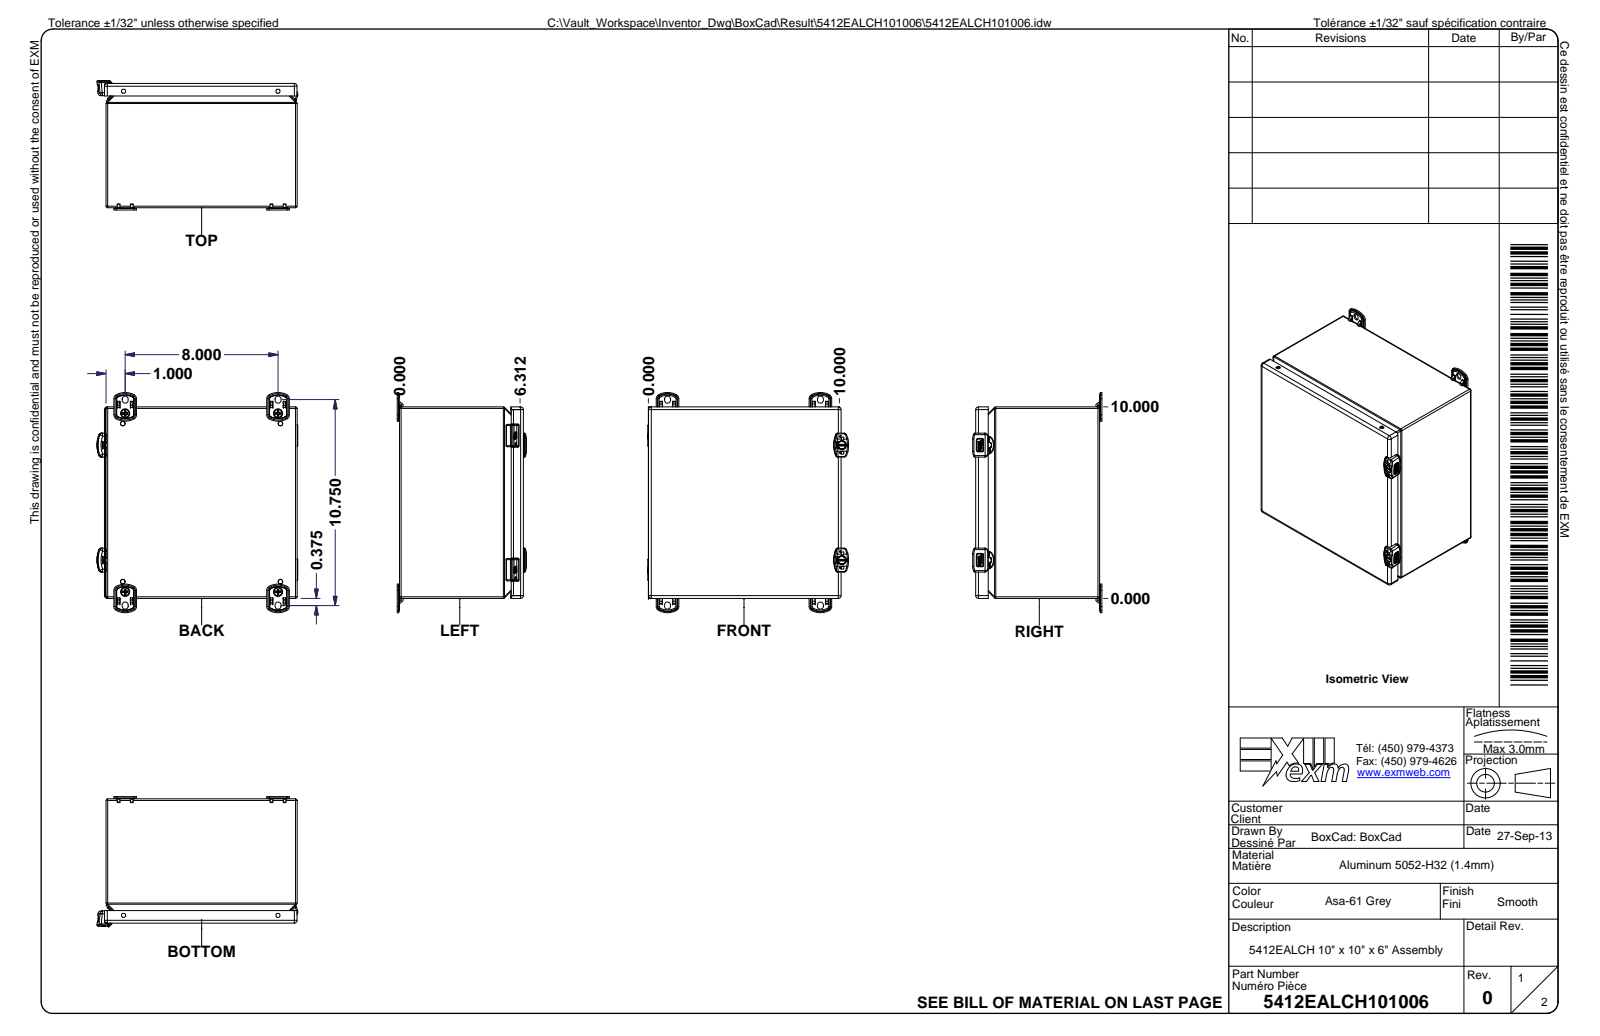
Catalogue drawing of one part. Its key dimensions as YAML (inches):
part_name: "5412EALCH101006; 5412EALCH101006B; 5412EALCH101006B-P; RIVET_NUT_SS_M6_FH_CE (+8 more)"
step_written_by: "Autodesk Inventor 2024 (AUTOMOTIVE_DESIGN)"
units: inches
bodies: {solids: 53, faces: 7459, planar: 3251, cylindrical: 1778, other: 2430}
overall_size: [11.496, 10.441, 6.756]
volume: 34.84
surface_area: 1244
round_holes:
  - {diameter: 0.197, count: 4}
  - {diameter: 0.197, count: 4}
  - {diameter: 0.236, count: 4}
  - {diameter: 0.32, count: 4}
  - {diameter: 0.03, count: 2}
  - {diameter: 0.165, count: 2}
  - {diameter: 0.173, count: 2}
  - {diameter: 0.175, count: 2}
  - {diameter: 0.201, count: 2}
  - {diameter: 0.218, count: 2}
  - {diameter: 0.23, count: 2}
  - {diameter: 0.236, count: 2}
round_bosses_or_shafts:
  - {diameter: 0.232, count: 8}
  - {diameter: 0.5, count: 4}
  - {diameter: 0.236, count: 4}
  - {diameter: 0.197, count: 3}
  - {diameter: 0.412, count: 2}
  - {diameter: 0.394, count: 2}
  - {diameter: 0.33, count: 2}
  - {diameter: 0.3, count: 2}
partial_cylinders:
  - {radius: 0.008, count: 224}
  - {radius: 0.02, count: 187}
  - {radius: 0.01, count: 100}
  - {radius: 0.004, count: 97}
  - {radius: 0.039, count: 89}
  - {radius: 0.059, count: 59}
  - {radius: 0.031, count: 33}
  - {radius: 0.012, count: 28}
face_to_face_distances: [0.053, 9.947, 6.429, 10, 9.894, 6.376, 6.482, 0.236, 0.304, 0.357]
hole_center_spacings: [8.25, 8.25, 0.546, 8.142, 8.781, 11.963, 11.963, 0.545]
